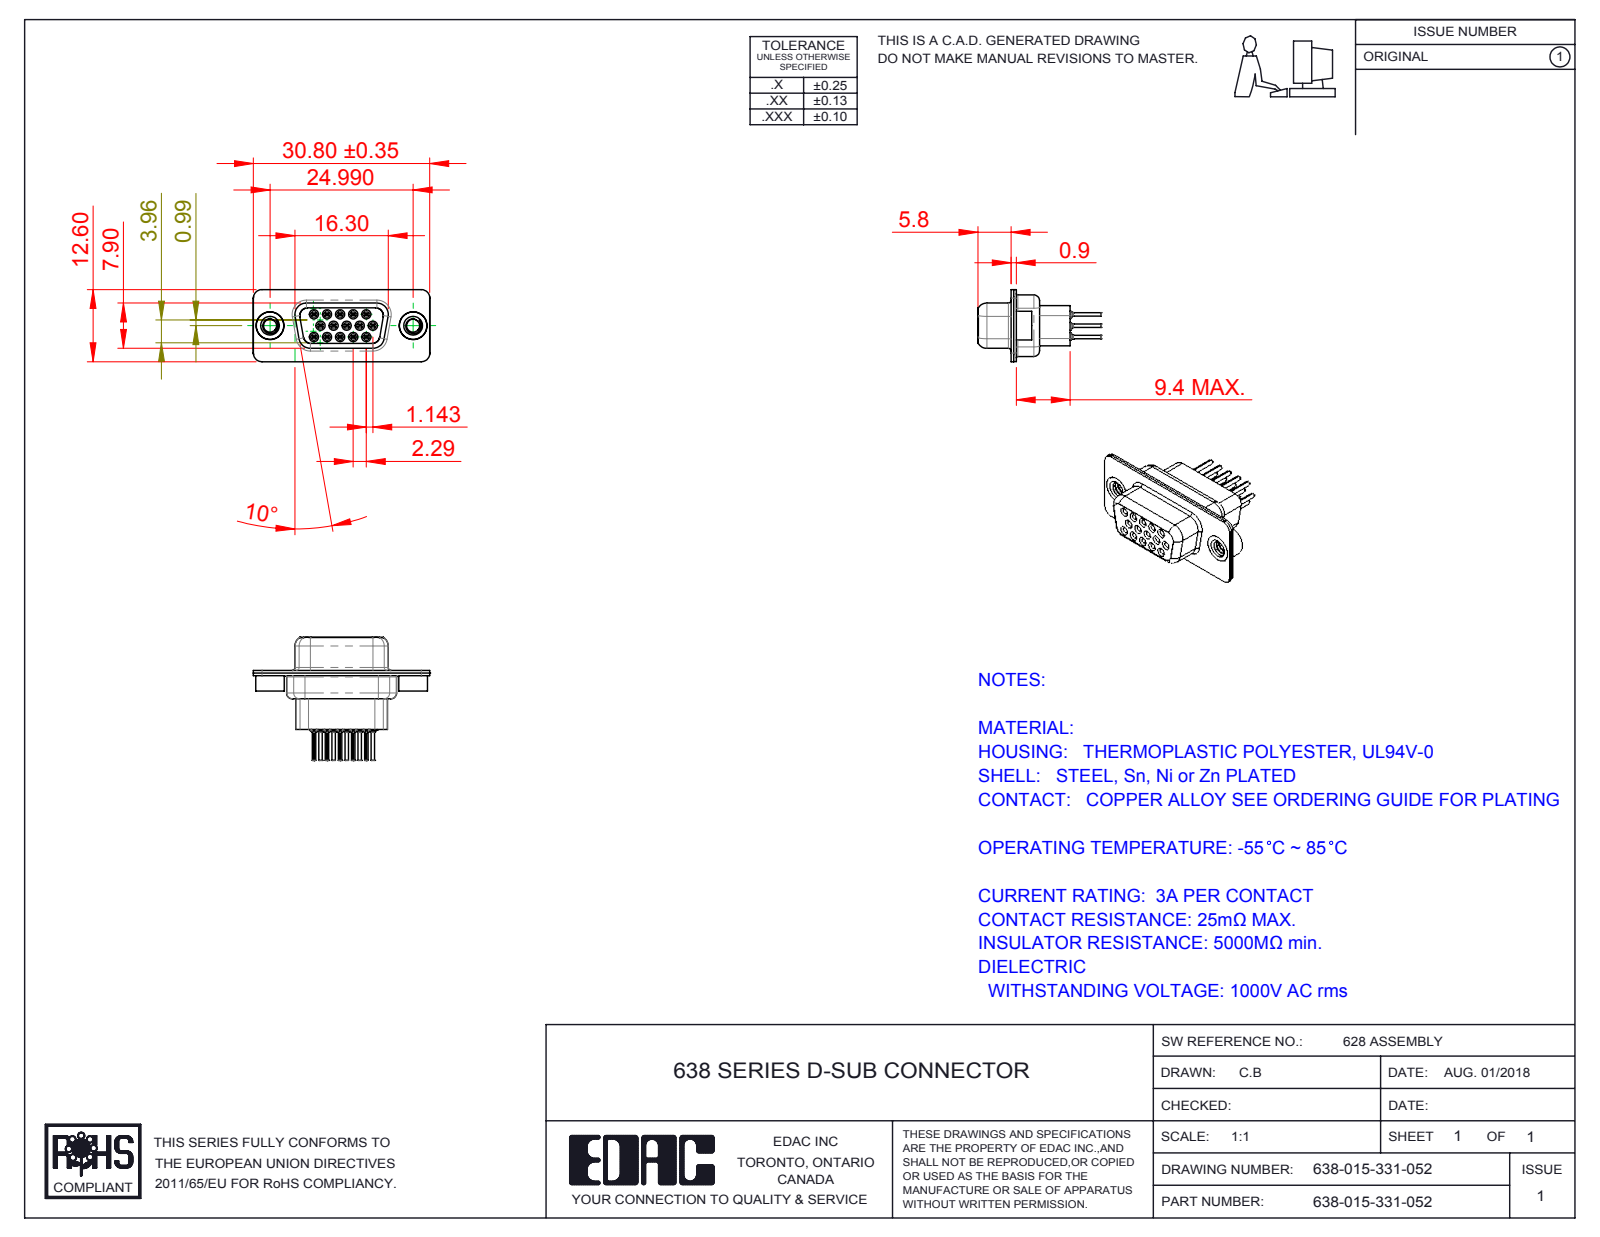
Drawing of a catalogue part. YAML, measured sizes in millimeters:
part_name: "638 4-40 Threaded Rivet; 638 Contact Row 1_31H; 638-015-331-052; 638 Shell Rear_15 Contacts (+4 more)"
step_written_by: "SolidWorks 2016 (CONFIG_CONTROL_DESIGN)"
units: millimeters
bodies: {solids: 20, faces: 2124, planar: 532, cylindrical: 632, other: 960}
overall_size: [30.81, 21.5, 12.6]
volume: 1884
surface_area: 6531
round_holes:
  - {diameter: 0.2, count: 15}
  - {diameter: 0.8, count: 15}
  - {diameter: 1, count: 15}
  - {diameter: 1.1, count: 15}
  - {diameter: 1.6, count: 15}
  - {diameter: 1.7, count: 15}
  - {diameter: 1.8, count: 15}
  - {diameter: 2, count: 2}
  - {diameter: 2.26, count: 2}
  - {diameter: 4, count: 2}
  - {diameter: 4.05, count: 2}
  - {diameter: 4.85, count: 2}
round_bosses_or_shafts:
  - {diameter: 2, count: 15}
  - {diameter: 1.5, count: 15}
  - {diameter: 1.2, count: 15}
  - {diameter: 0.6, count: 15}
  - {diameter: 5, count: 2}
  - {diameter: 4.95, count: 2}
  - {diameter: 4.8, count: 2}
partial_cylinders:
  - {radius: 0.1, count: 30}
  - {radius: 1.5, count: 20}
  - {radius: 2, count: 12}
  - {radius: 0.28, count: 10}
  - {radius: 1.55, count: 8}
  - {radius: 1.35, count: 5}
  - {radius: 0.25, count: 4}
  - {radius: 0.5, count: 4}
face_to_face_distances: [0.45, 0.9, 0.4, 1.43, 8.88, 6.6, 7, 2.28, 9.4, 5.8]
hole_center_spacings: [3.96, 2.28, 4.57, 2.29, 6.05, 6.04, 6.86, 7.92]
